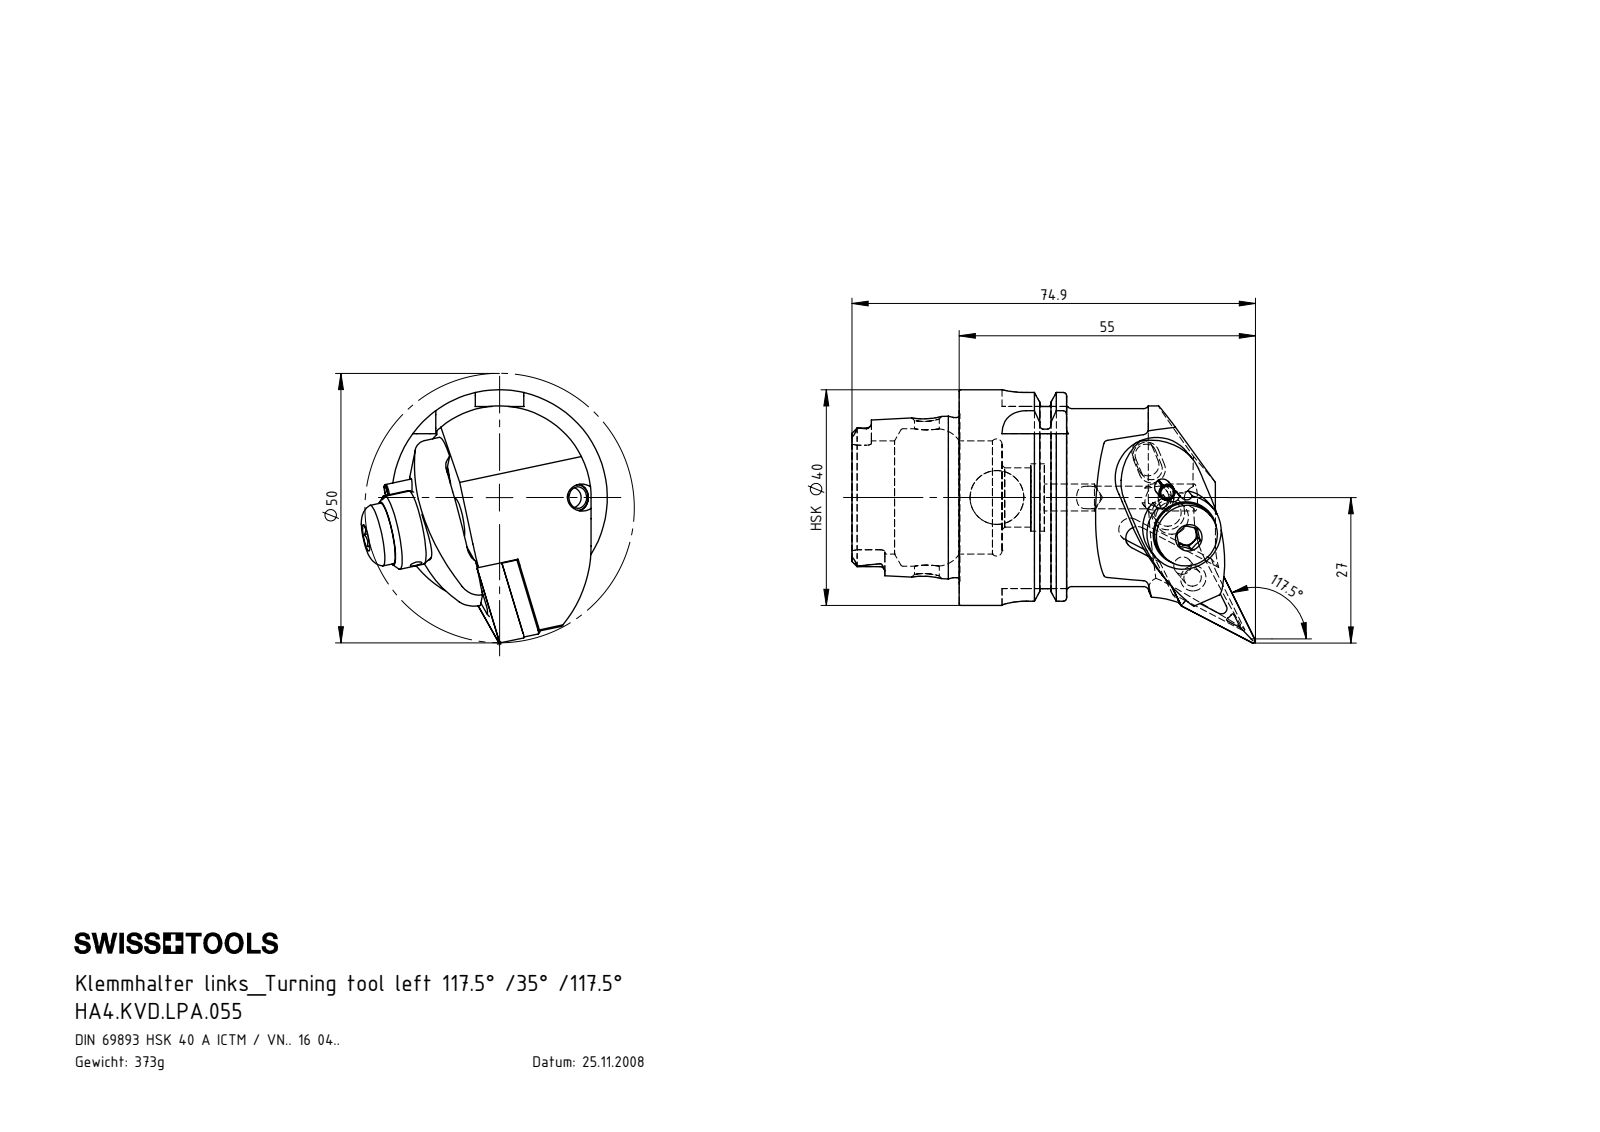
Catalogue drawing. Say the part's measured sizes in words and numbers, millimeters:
The part is named "WCC-ER5.102.012_B; ISO 13337 - 3 x 12_PreviewCfg; KVT_MB_600_050; VNMG160404 (+7 more)". Its 3-D file was written by "SolidWorks 2017 (AUTOMOTIVE_DESIGN)". It is 11 solids with 465 faces: 126 planar, 152 cylindrical and 187 other. Overall it measures 74.9 by 47 by 45.65 millimeters. Its volume is 46 977 cubic millimeters and its surface area 18 586 square millimeters. Round holes: 3 of diameter 2, 3 of diameter 5, 2 of diameter 7, 1 of diameter 2.4, 1 of diameter 3, 1 of diameter 3.3, 1 of diameter 3.8, 1 of diameter 4, 1 of diameter 4.2, 1 of diameter 4.6, 1 of diameter 4.95, 1 of diameter 6.2. Round bosses or shafts: 2 of diameter 5, 2 of diameter 3, 1 of diameter 40, 1 of diameter 34.75, 1 of diameter 33, 1 of diameter 29.71, 1 of diameter 14, 1 of diameter 11.5. Partial cylindrical surfaces (rounded edges, fillets, slot ends): 6 of radius 0.39, 6 of radius 0.9, 4 of radius 0.4, 4 of radius 4.5, 3 of radius 0.69, 3 of radius 0.69, 3 of radius 1.5, 3 of radius 17. The main face-to-face distances are 7.63, 3.18, 4.45, 7.95, 1.31, 12, 8.94, 5.76, 19.95, 9.53. The hole center spacings are 8.02, 14.3, 22.32, 8.01, 8.03, 8.19, 8.2, 14.12.
